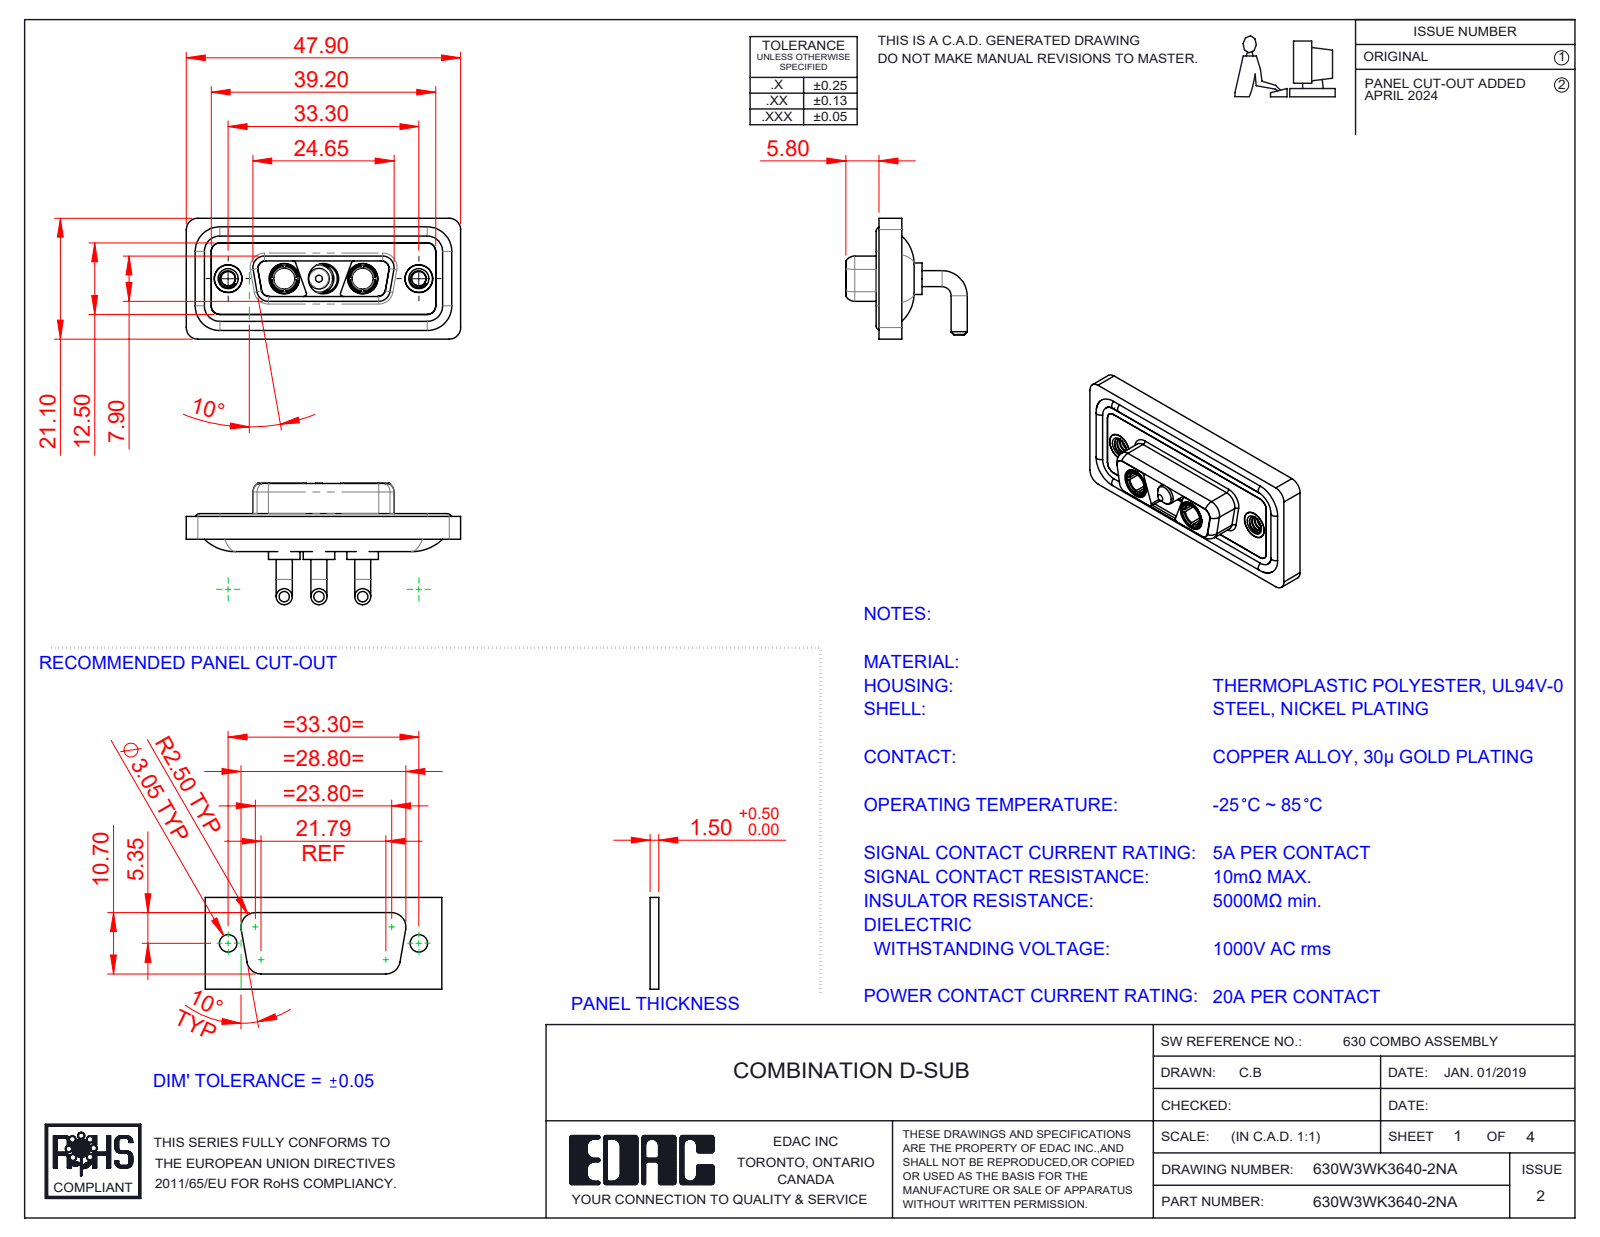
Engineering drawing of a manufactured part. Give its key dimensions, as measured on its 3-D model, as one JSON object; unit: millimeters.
{"part_name": "630Combo Threaded Rivet_A; 630Combo Shell Front_15 Contacts; 630W3WK3640-2NA; Power Pin_20A RA (+4 more)", "step_written_by": "SolidWorks 2023 (CONFIG_CONTROL_DESIGN)", "units": "millimeters", "bodies": {"solids": 13, "faces": 589, "planar": 178, "cylindrical": 262, "other": 149}, "overall_size": [47.9, 21.2, 21.1], "volume_mm3": 6024, "surface_area_mm2": 9741, "round_holes": [[4.85, 5], [5.3, 3], [2.5, 2], [3.7, 2], [4, 2], [4.05, 2], [5, 2]], "round_bosses_or_shafts": [[2.8, 6], [1.6, 4], [5.5, 3], [5.2, 3], [4.75, 3], [3.75, 3], [4.96, 2], [4.95, 2]], "partial_cylinders_radius": [[2, 20], [1.5, 18], [1.35, 12], [0.5, 8], [1.6, 8], [0.25, 4], [0.6, 4], [0.65, 4]], "face_to_face_distances": [0.4, 1.8, 1.1, 1.6, 2.9, 2.5, 3.1, 3.7, 4.1, 1.5], "hole_center_spacings": [6.85, 9.8, 16.65, 23.5, 13.7, 33.3]}
